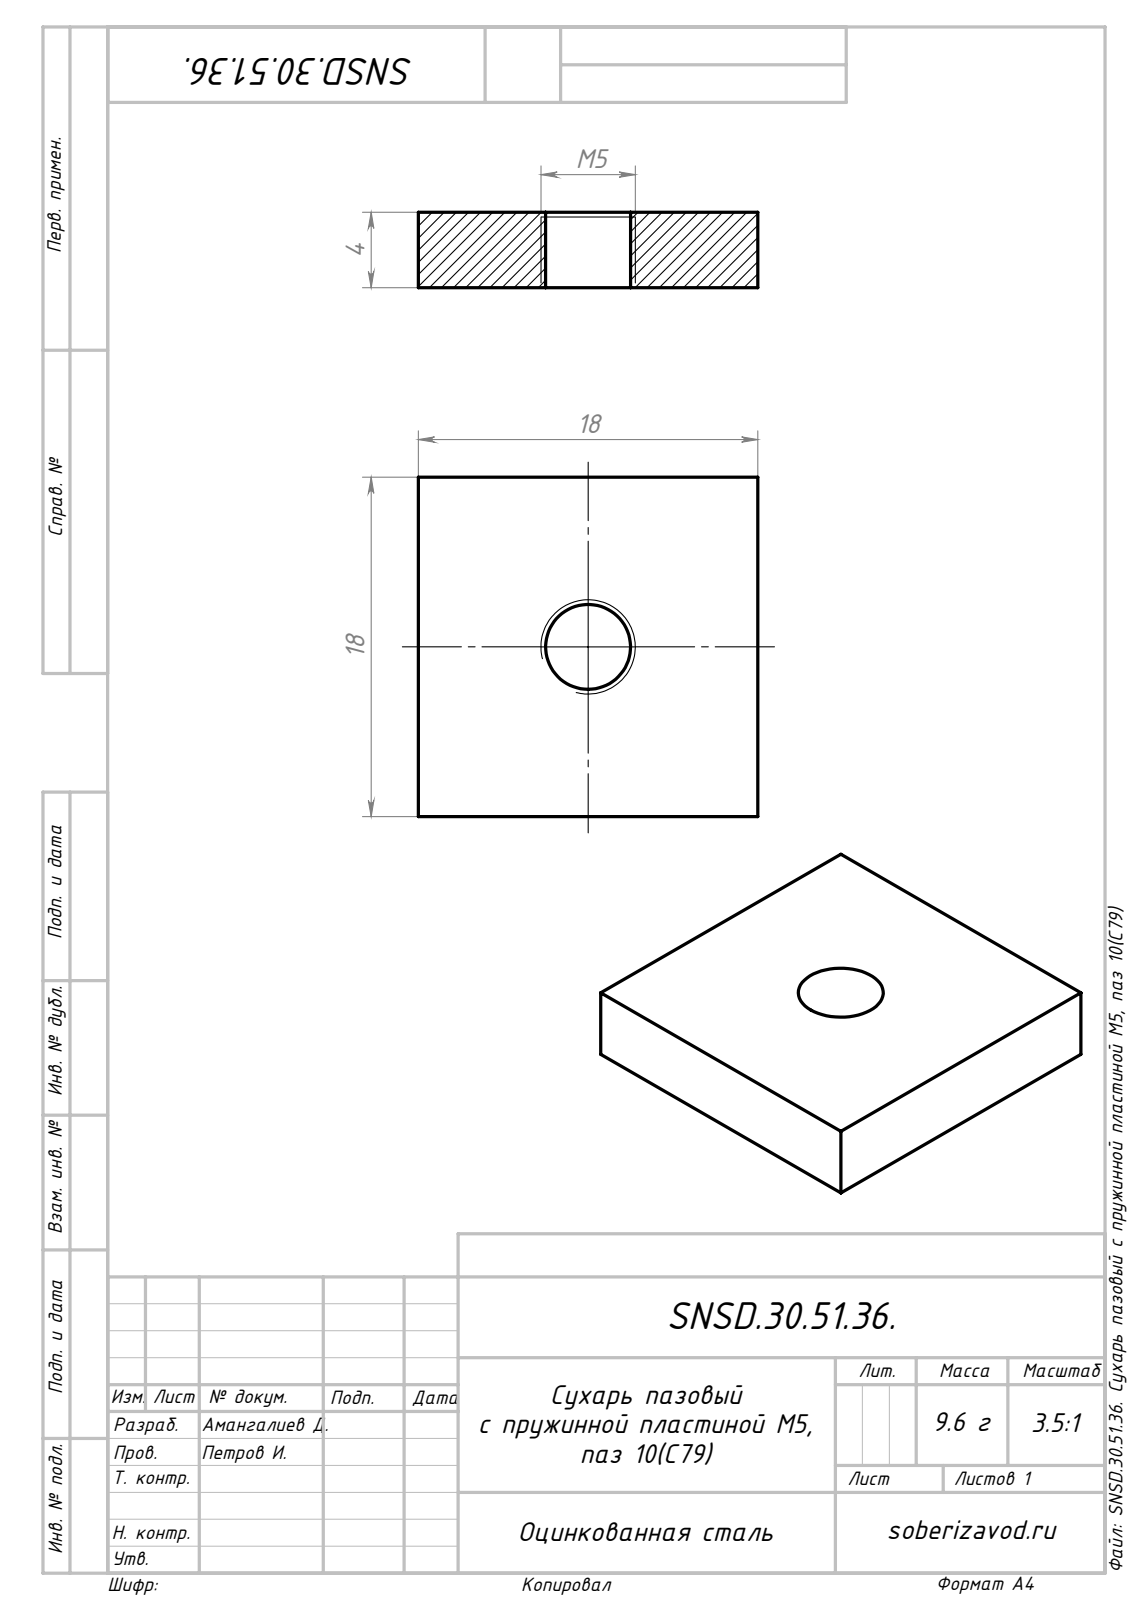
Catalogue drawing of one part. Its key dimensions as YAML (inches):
part_name: "SNSD.30.51.36. Сухарь пазовый с пружинной пластиной M5, паз 10(C79); SNSD.30.51.19. Сухарь пазовый с пружинной пластиной M6, паз 8(B79)B80B78B81C79_00"
step_written_by: "SolidWorks 2017 (AUTOMOTIVE_DESIGN)"
units: inches
bodies: {solids: 1, faces: 8, planar: 6, cylindrical: 2, other: 0}
overall_size: [0.709, 0.709, 0.157]
volume: 0.075
surface_area: 1.49
round_holes:
  - {diameter: 0.177, count: 1}
face_to_face_distances: [0.157, 0.709]
